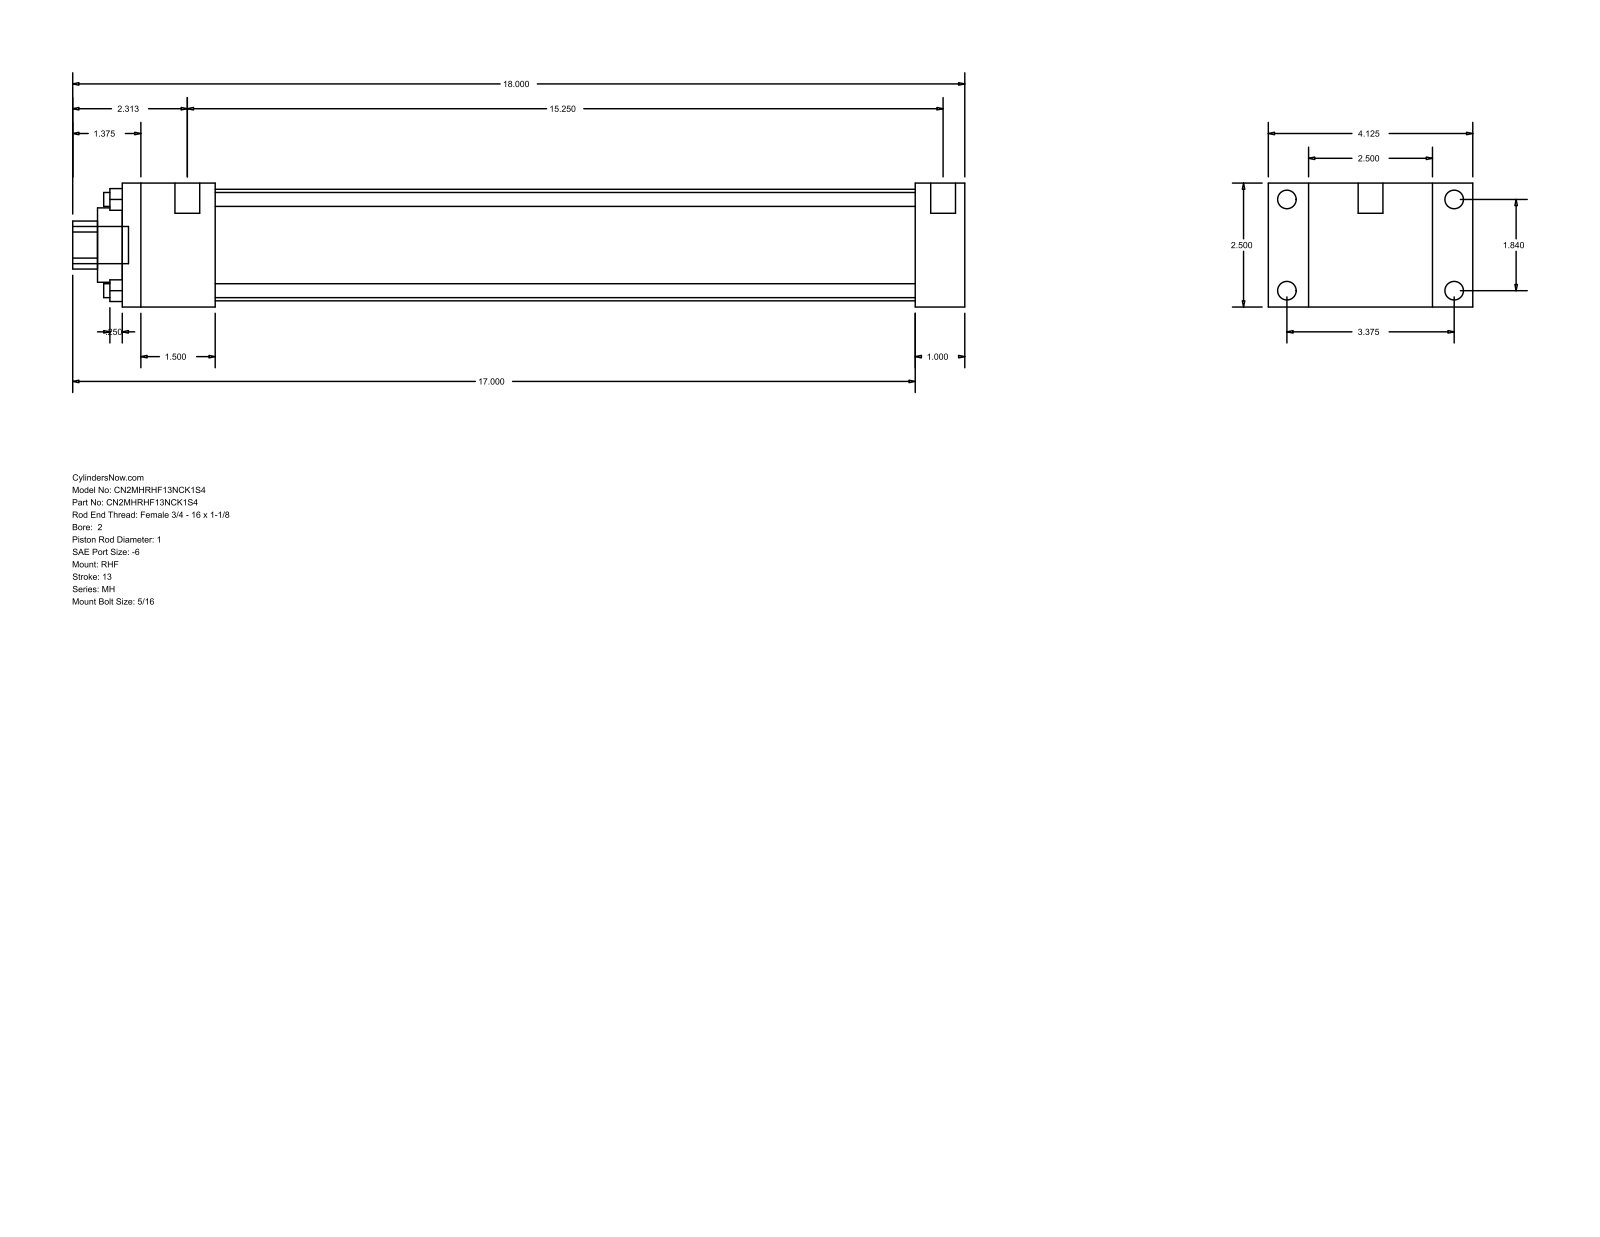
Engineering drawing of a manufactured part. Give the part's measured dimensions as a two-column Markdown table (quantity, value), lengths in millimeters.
| quantity | value |
| --- | --- |
| part name | MH_RHF__0200_1 |
| STEP written by | GSSL Pune (CONFIG_CONTROL_DESIGN) |
| units | millimeters |
| bodies | 0 solids, 88 faces (60 planar, 28 cylindrical, 0 other) |
| overall size | 457.2 × 104.78 × 63.5 |
| round holes (diameter × count) | 7.14 × 4, 25.4 × 1, 38.1 × 1, 57.15 × 1 |
| round bosses / shafts (diameter × count) | 9.53 × 4, 5.56 × 4, 12.7 × 2, 19.05 × 1 |
| partial cylindrical surfaces (radius × count) | 12.29 × 1 |
| main face-to-face distances | 63.5, 25.4, 20.64, 84.14, 431.8, 406.4, 104.78, 47.63, 358.77, 384.17 |
| hole center spacings | 33.05, 46.74, 66.1 |
